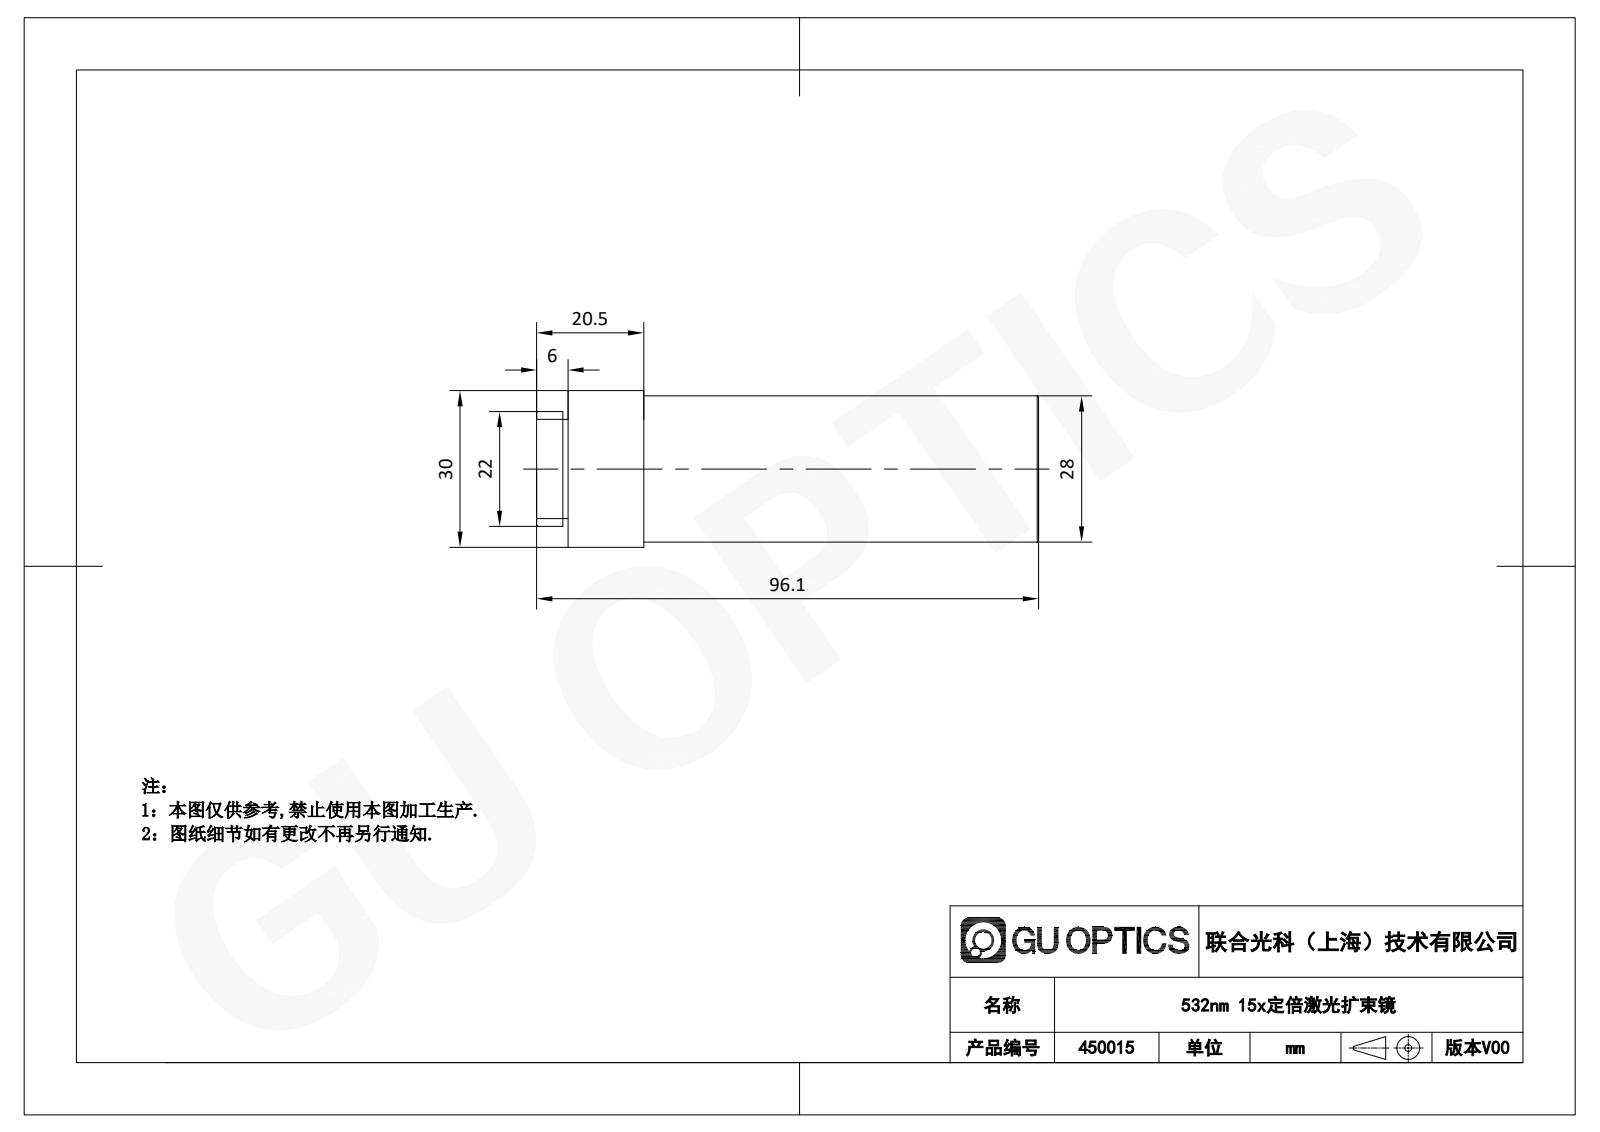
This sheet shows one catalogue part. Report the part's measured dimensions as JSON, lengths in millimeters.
{"part_name": "450015", "step_written_by": "SolidWorks 2020 (AUTOMOTIVE_DESIGN)", "units": "millimeters", "bodies": {"solids": 1, "faces": 32, "planar": 8, "cylindrical": 16, "other": 8}, "overall_size": [96.1, 30, 30], "volume_mm3": 45763, "surface_area_mm2": 14095, "round_holes": [[6, 1], [18, 1]], "round_bosses_or_shafts": [[30, 1], [28, 1], [22, 1], [19, 1]], "face_to_face_distances": [90.1, 6, 96.1, 4, 92.1, 86.1, 46.1, 40.1, 46, 50]}
